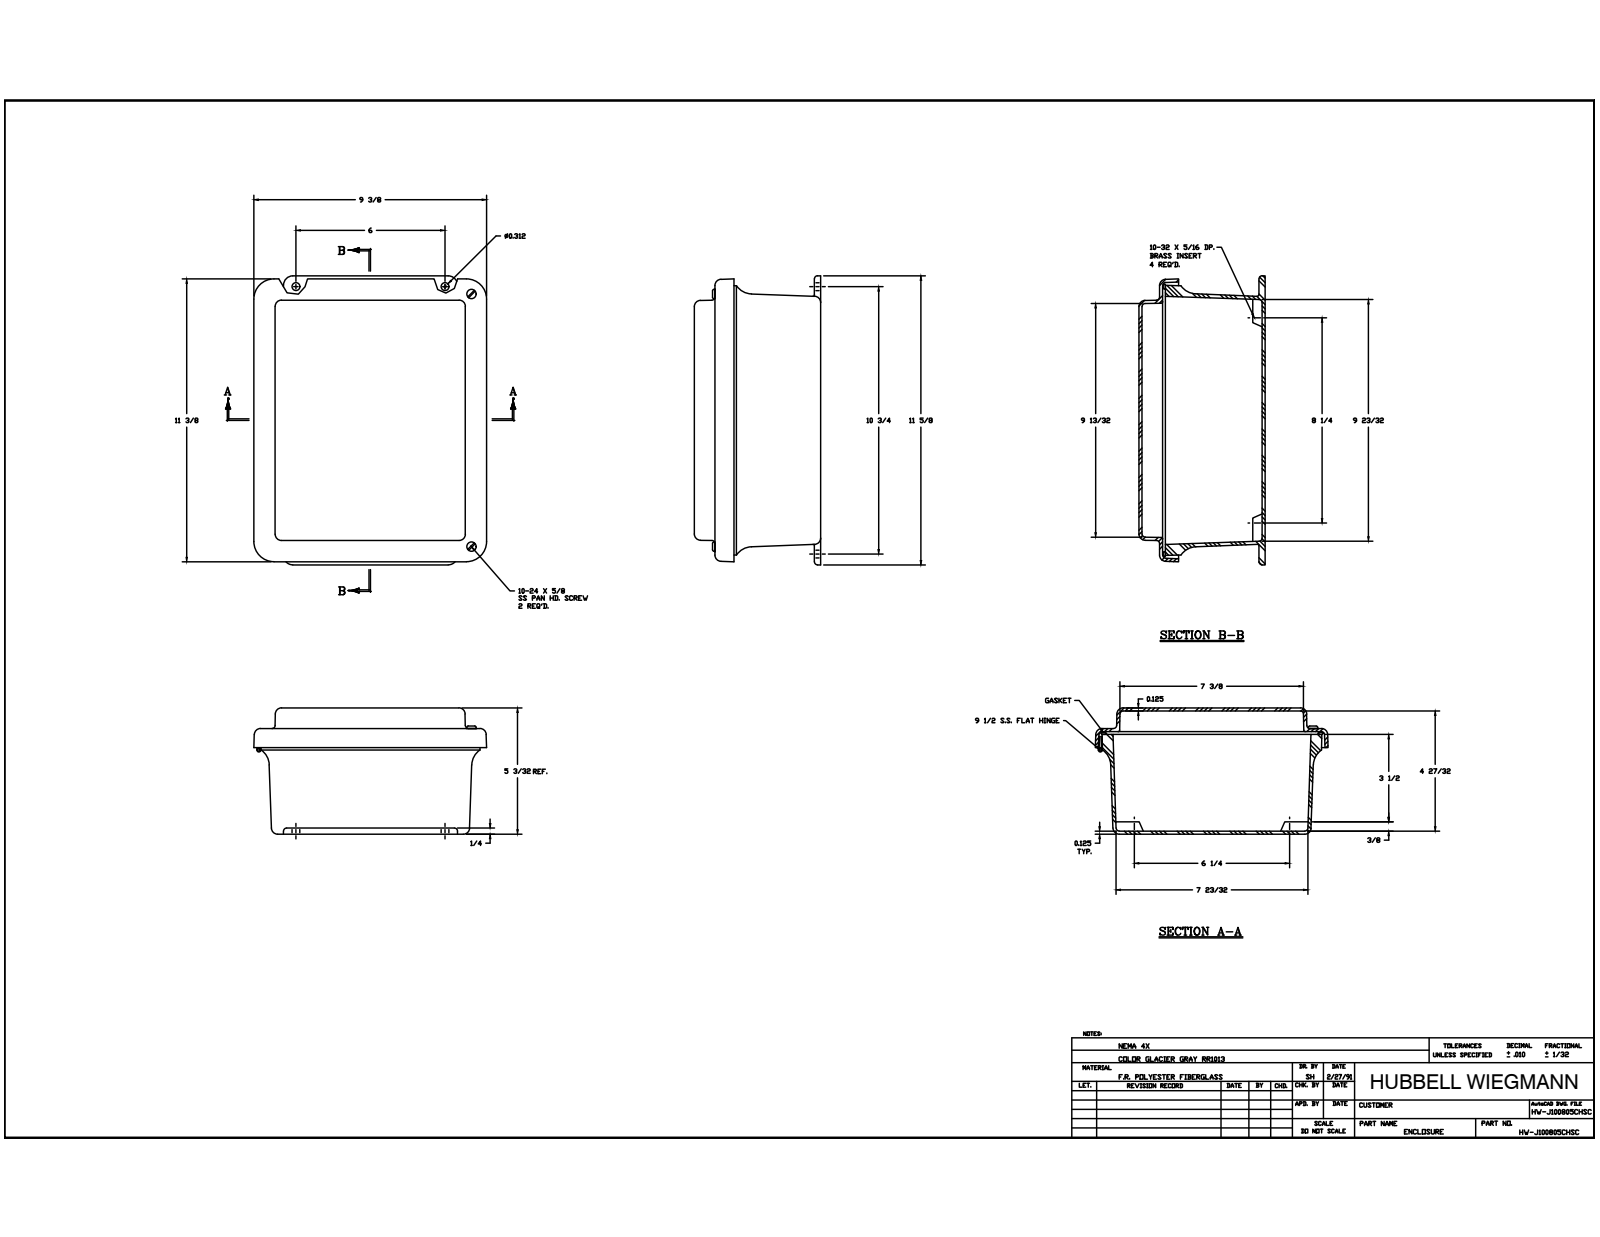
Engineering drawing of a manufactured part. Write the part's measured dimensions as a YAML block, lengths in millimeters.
part_name: "J1008HW_1; RMINS45821P_17; RMINS45821P_18; RMINS45821P_19 (+8 more)"
step_written_by: "Autodesk Inventor 2014 (AUTOMOTIVE_DESIGN)"
units: millimeters
bodies: {solids: 22, faces: 809, planar: 269, cylindrical: 307, other: 233}
overall_size: [295.27, 238.59, 128.62]
volume: 1017000
surface_area: 549619
round_holes:
  - {diameter: 3.33, count: 8}
  - {diameter: 3.56, count: 8}
  - {diameter: 3.86, count: 5}
  - {diameter: 3.96, count: 4}
  - {diameter: 5.54, count: 4}
  - {diameter: 3.68, count: 2}
  - {diameter: 2.16, count: 1}
  - {diameter: 2.16, count: 1}
round_bosses_or_shafts:
  - {diameter: 6.35, count: 8}
  - {diameter: 3.17, count: 8}
  - {diameter: 6.86, count: 6}
  - {diameter: 4.83, count: 2}
  - {diameter: 3.97, count: 2}
  - {diameter: 3.94, count: 1}
partial_cylinders:
  - {radius: 3.17, count: 24}
  - {radius: 0.79, count: 20}
  - {radius: 6.35, count: 12}
  - {radius: 5.08, count: 6}
  - {radius: 9.53, count: 4}
  - {radius: 19.05, count: 4}
  - {radius: 1.6, count: 2}
face_to_face_distances: [3.18, 3.17, 122.27, 125.44, 128.62, 125.45, 21.06, 101.21, 104.38, 24.24]
hole_center_spacings: [152.4, 76.2, 6.35, 63.5, 69.85, 158.75, 33.96, 82.55]
